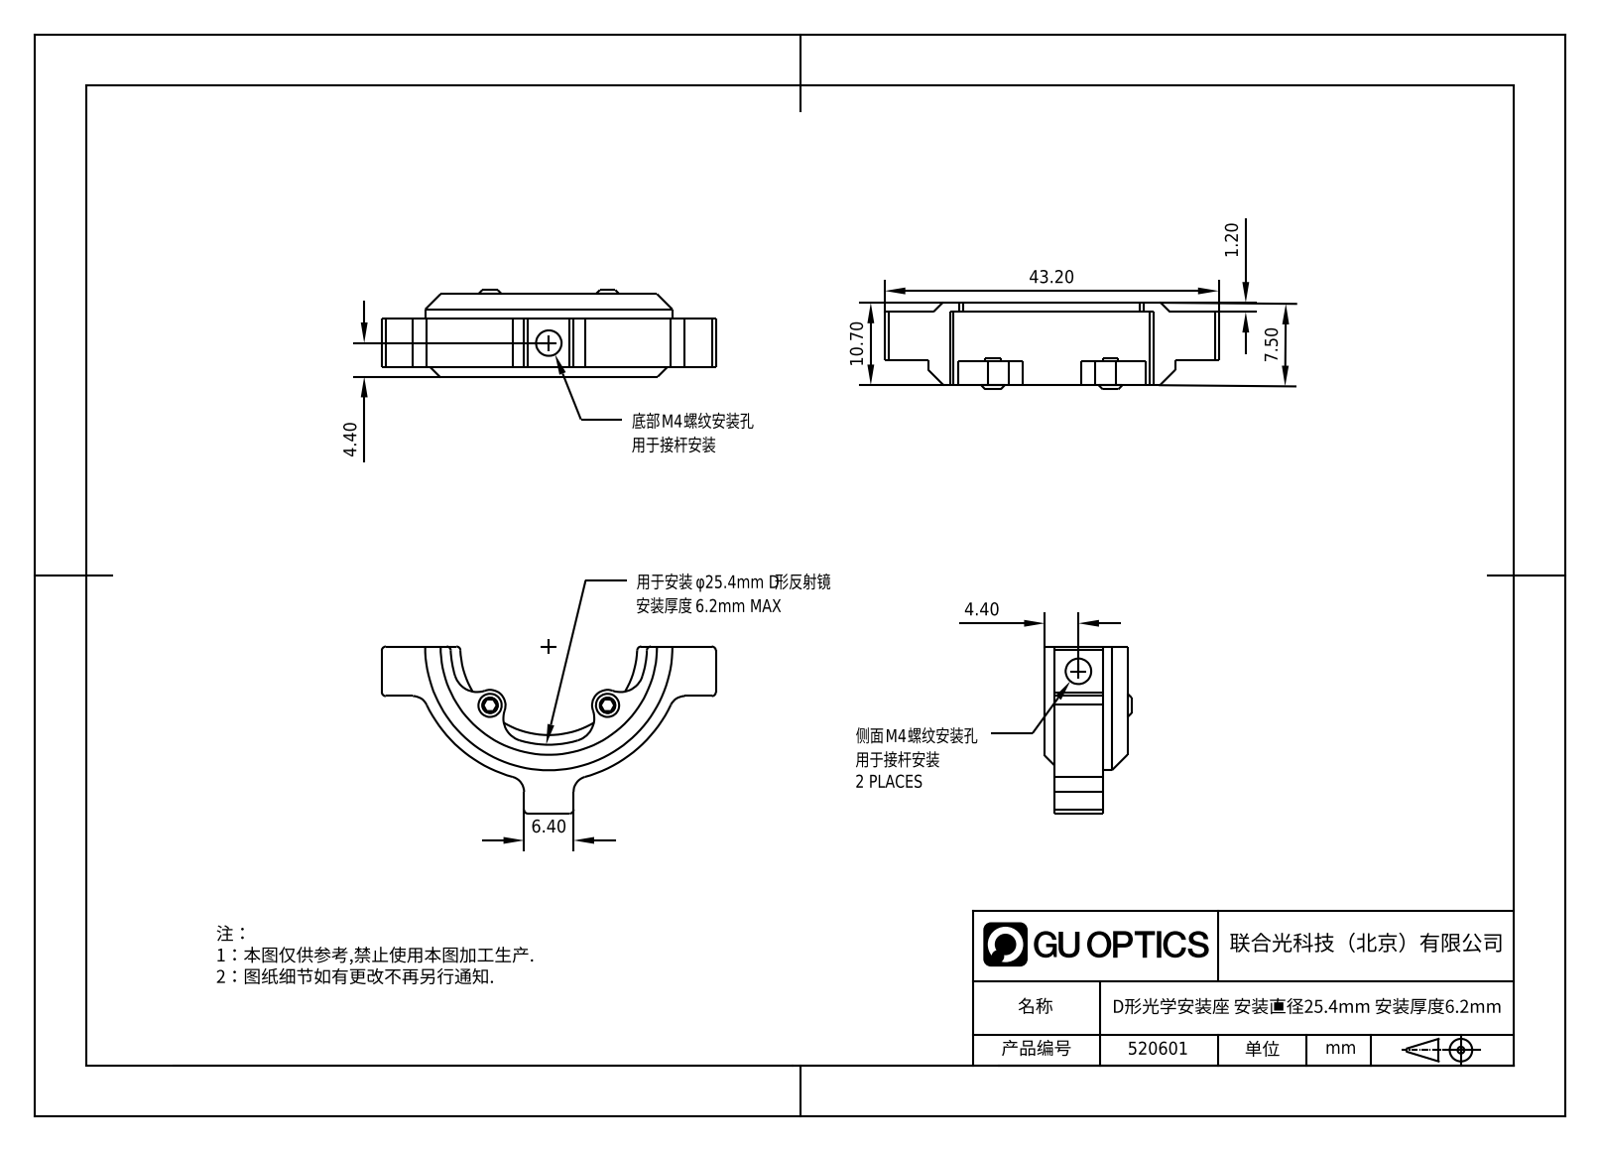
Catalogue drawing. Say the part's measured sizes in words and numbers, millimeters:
The part is named "1.3.12.2_ZZM-1.0". Its 3-D file was written by "SolidWorks 2021 (CONFIG_CONTROL_DESIGN)". It is 3 solids with 99 faces: 34 planar, 45 cylindrical and 20 other. Overall it measures 43.2 by 21.6 by 11.22 millimeters. Its volume is 2 454 cubic millimeters and its surface area 2 285 square millimeters. Round holes: 2 of diameter 2.5, 2 of diameter 3.3. Round bosses or shafts: 2 of diameter 3, 2 of diameter 2. Partial cylindrical surfaces (rounded edges, fillets, slot ends): 10 of radius 0.5, 6 of radius 2, 4 of radius 3, 1 of radius 11.45, 1 of radius 12.7, 1 of radius 16, 1 of radius 17.5. The main face-to-face distances are 6.3, 7.5, 1.2, 6.4, 3.2, 9.5, 10.7, 3.1, 7.6, 18.4. The hole center spacings are 15.2.
